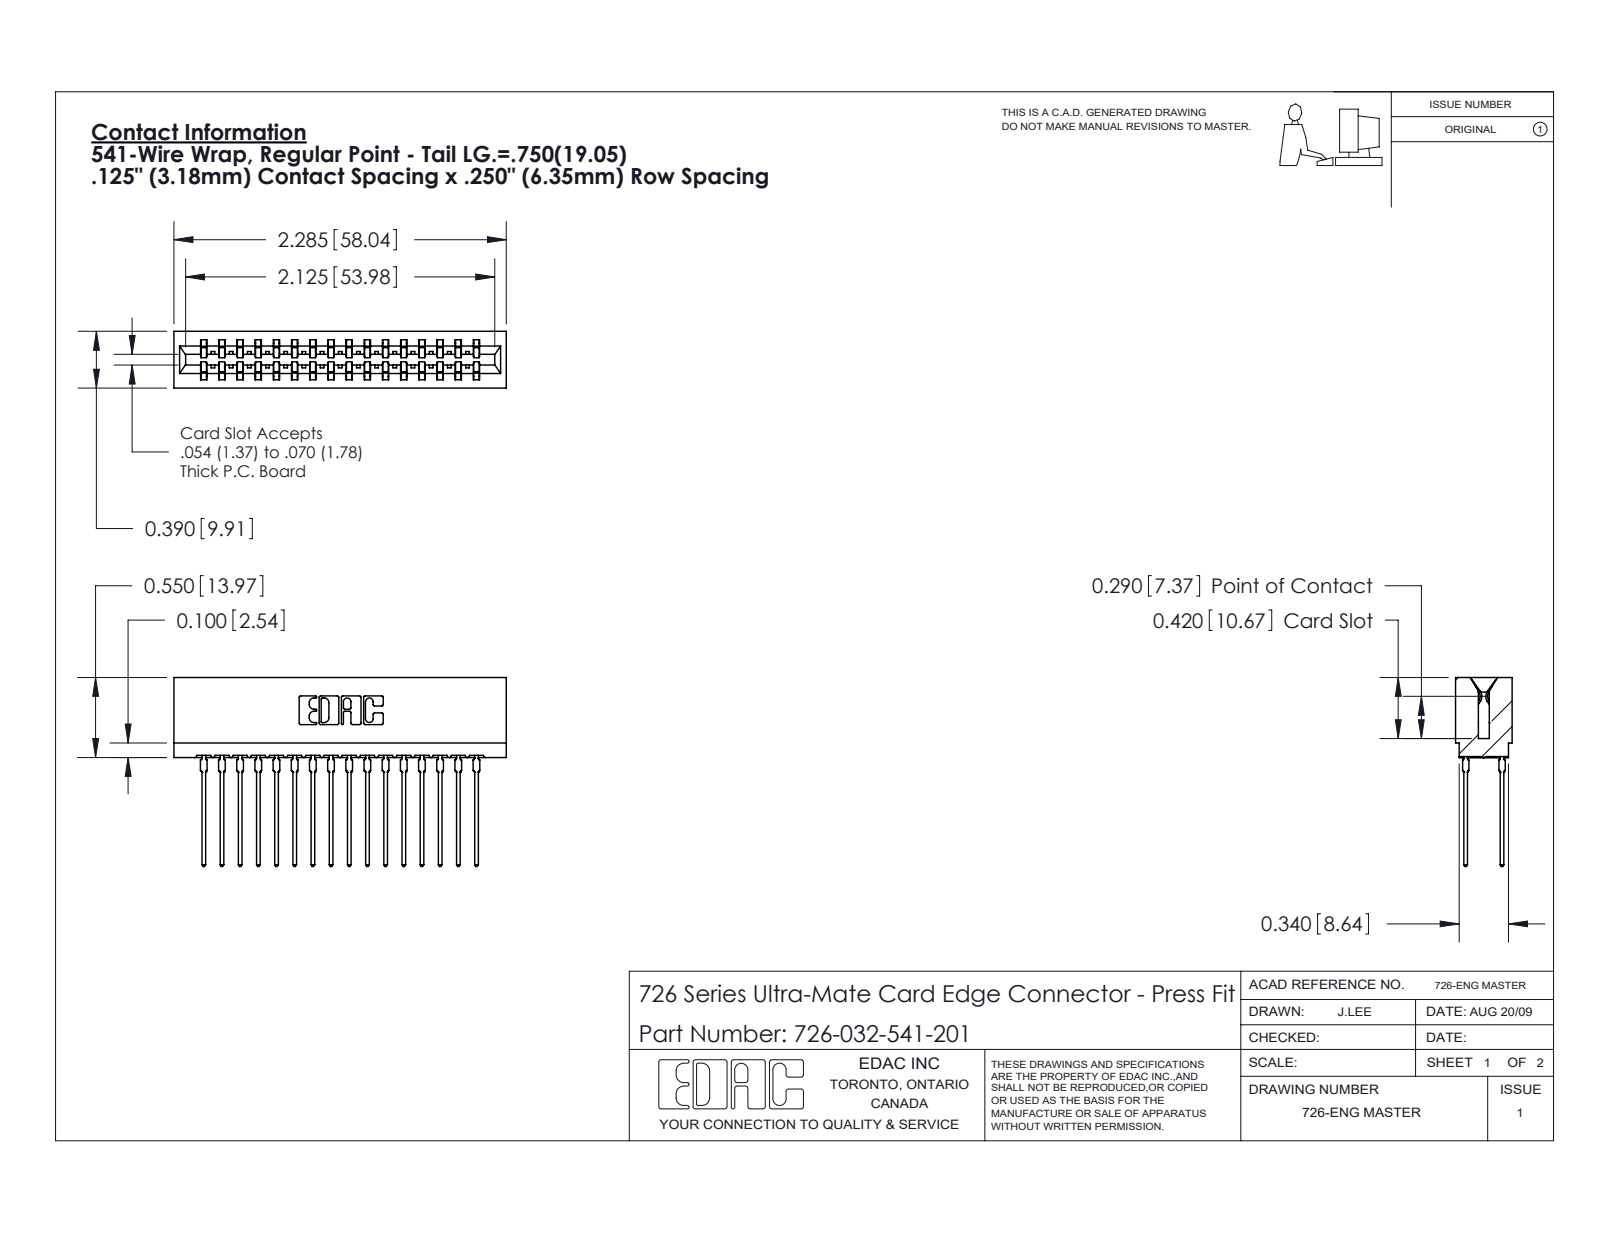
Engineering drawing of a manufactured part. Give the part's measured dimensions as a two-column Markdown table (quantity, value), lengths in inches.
| quantity | value |
| --- | --- |
| part name | 726-032-541-201; 746-292-001_541; 726 Part_.515 Slot Depth - 01 |
| STEP written by | SolidWorks 2020 (CONFIG_CONTROL_DESIGN) |
| units | inches |
| bodies | 33 solids, 2961 faces (1527 planar, 602 cylindrical, 832 other) |
| overall size | 2.285 × 1.299 × 0.39 |
| volume | 0.345 in³ |
| surface area | 15.16 in² |
| partial cylindrical surfaces (radius × count) | 0.021 × 64, 0.01 × 22, 0.015 × 17, 0.005 × 8, 0.011 × 8, 0.007 × 6, 0.031 × 6, 0.026 × 3 |
| main face-to-face distances | 0.057, 0.333, 0.25, 0.025, 0.307, 0.083, 0.5, 0.39, 0.275, 0.125 |
